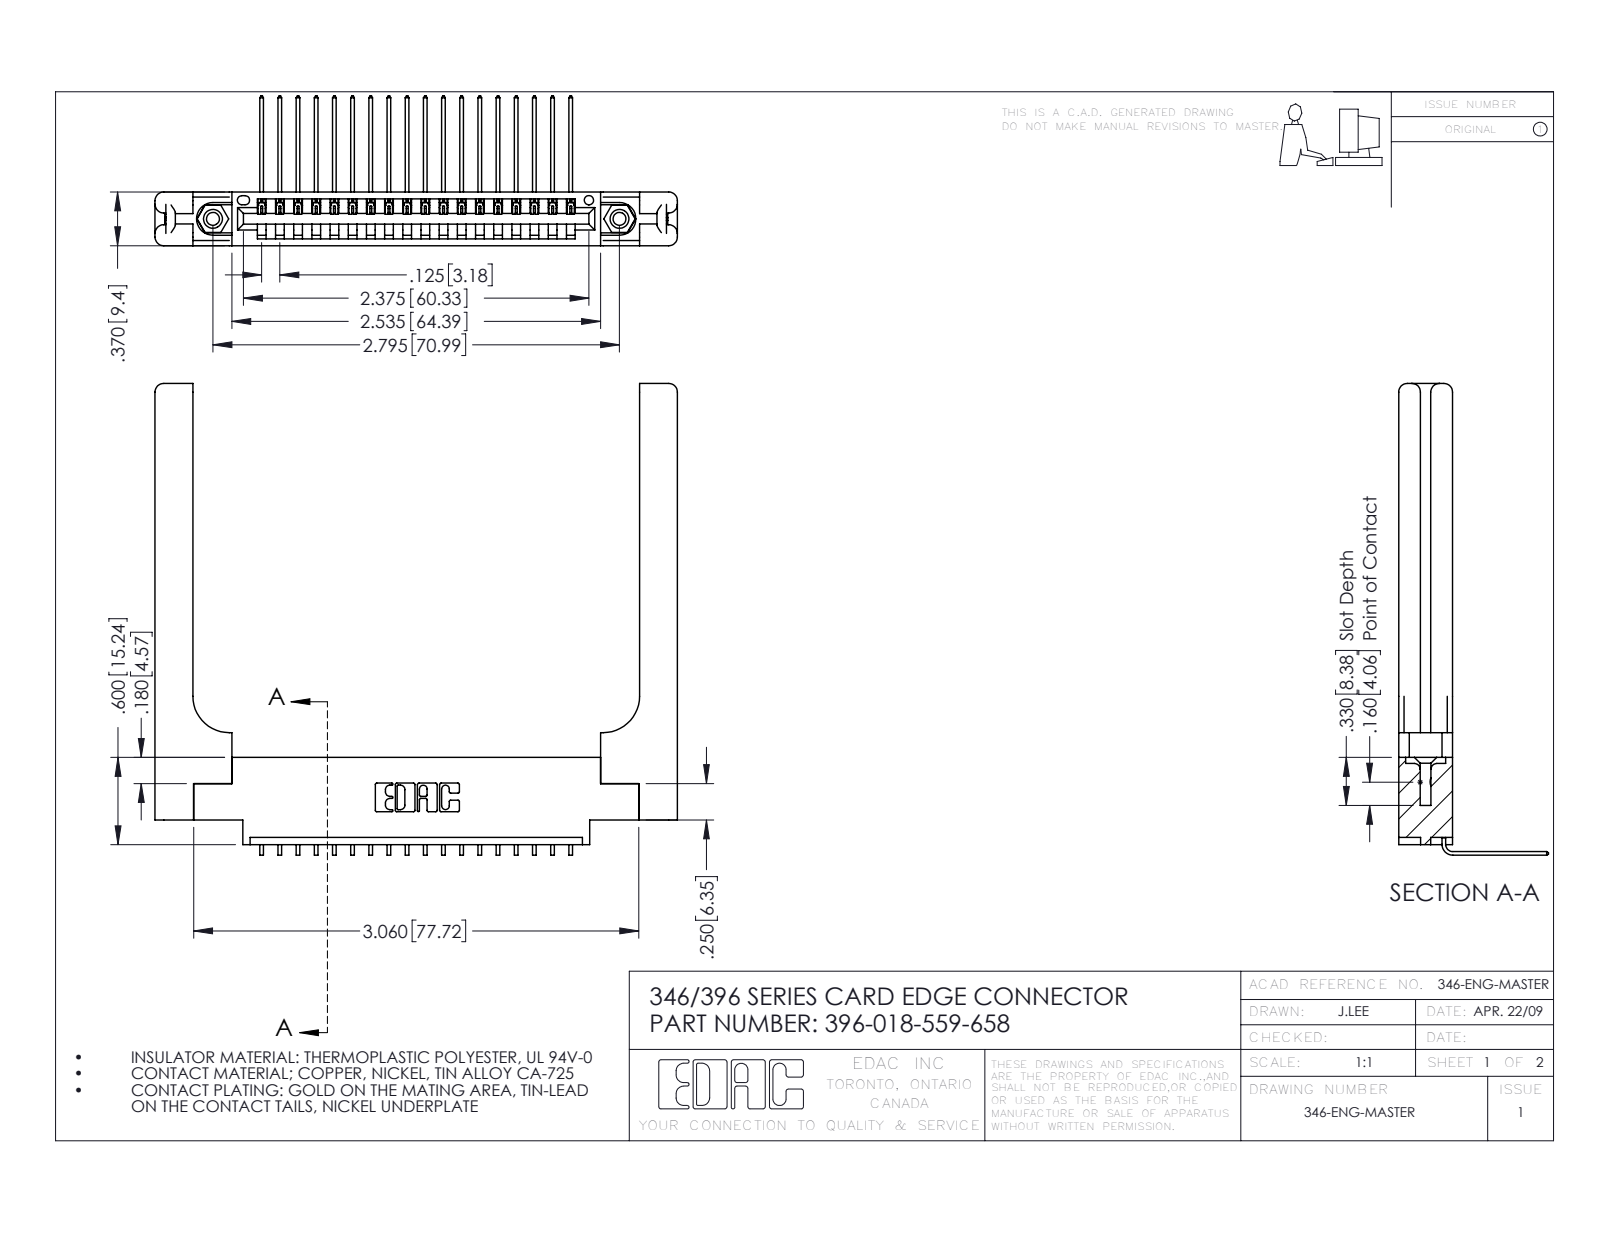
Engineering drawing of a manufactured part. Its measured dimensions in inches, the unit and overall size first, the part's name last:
Units: inches
Overall size (bounding box): 3.591 × 3.243 × 1.03
Round holes (diameter × count): ⌀0.089 ×2, ⌀0.125 ×2, ⌀0.156 ×2, ⌀0.064 ×1
Round bosses / shafts (diameter × count): ⌀0.155 ×2
Partial cylindrical surfaces — rounded edges, fillets, slot ends (radius × count): R0.006 ×36, R0.01 ×22, R0.06 ×16, R0.007 ×6, R0.031 ×6, R0.026 ×3, R0.03 ×2, R0.031 ×2
Main face-to-face distances: 0.37, 0.072, 0.15, 0.048, 0.148, 0.322, 0.25, 0.025, 0.102, 0.22
Hole centre spacings: 0.246, 2.588, 2.795
Volume: 0.976 in³ · Surface area: 24.83 in²
Bodies: 23 solids, 1462 faces (984 planar, 418 cylindrical, 60 other)
Part name (STEP PRODUCT): 346-220-058_345-220-058; 345-250-001_345-250-001-102; 396-018-559-658; 345-292-001_558 559 Tail - 1 (+1 more)
STEP written by: SolidWorks 2016 (CONFIG_CONTROL_DESIGN)
